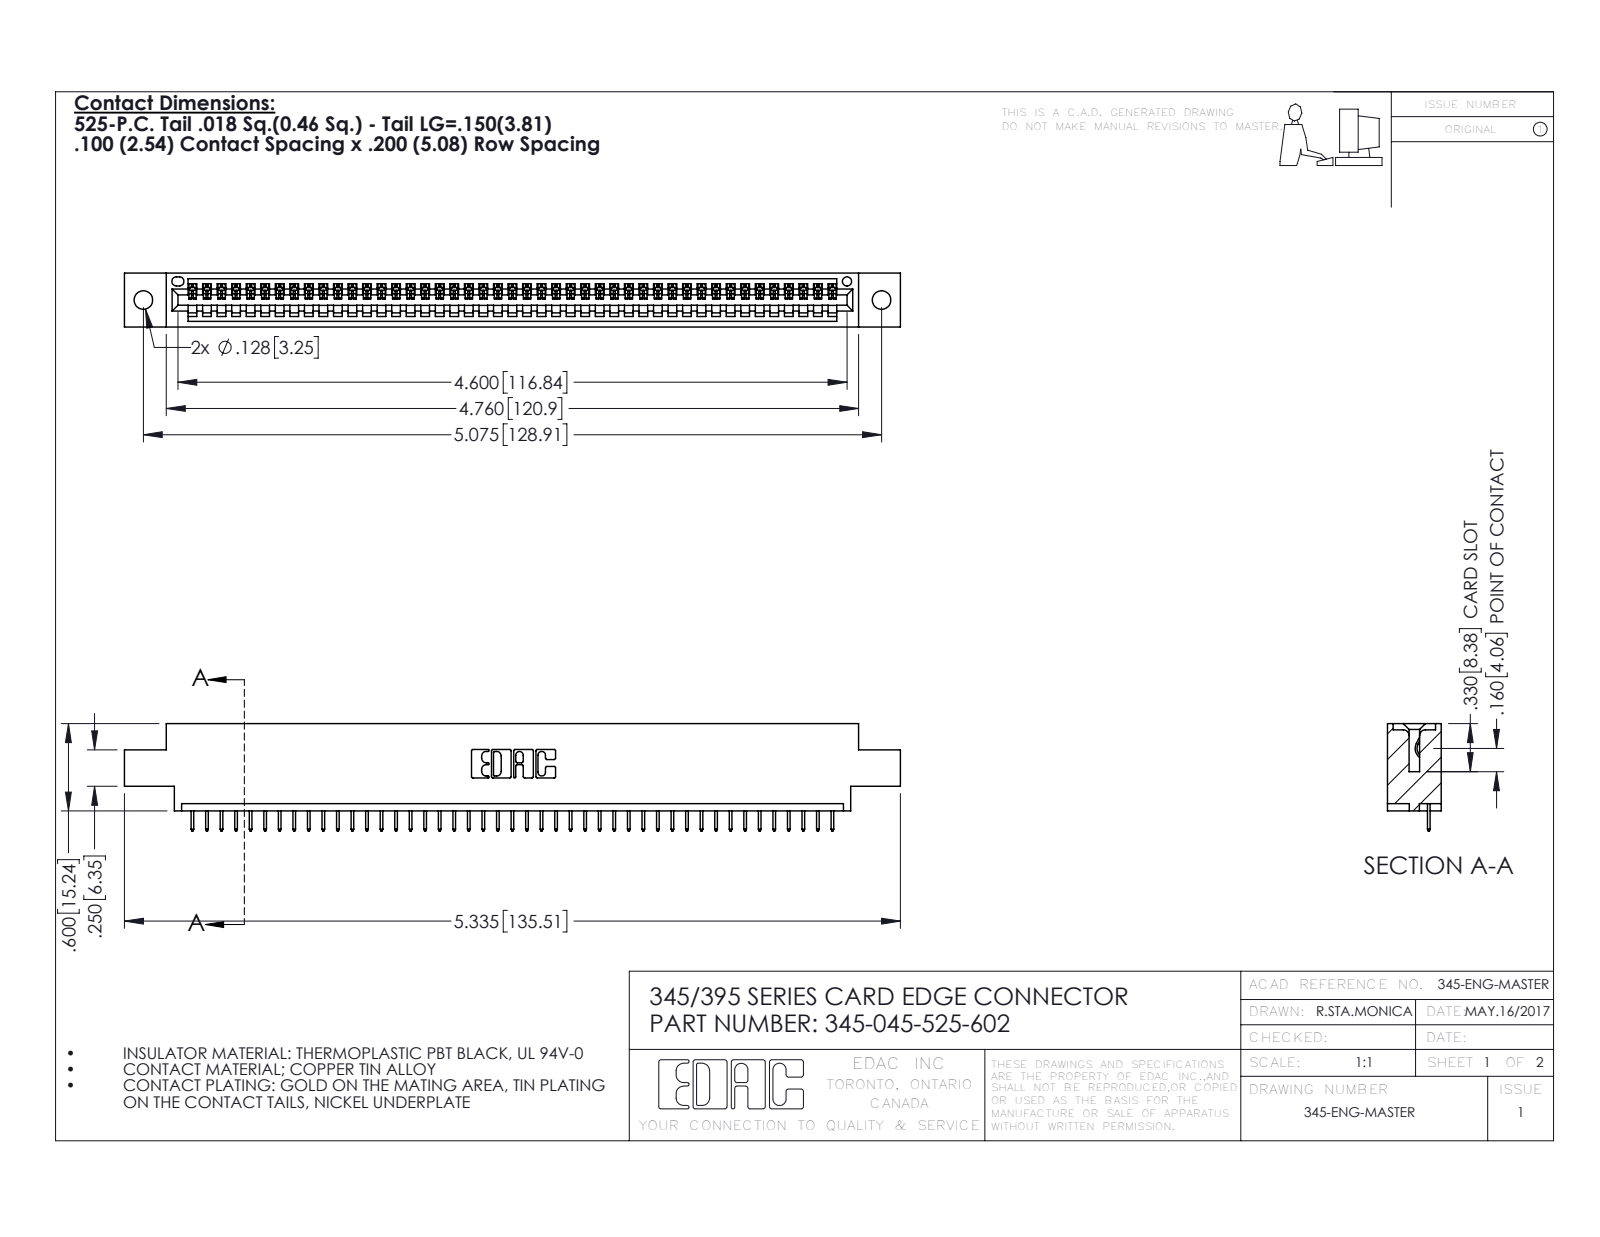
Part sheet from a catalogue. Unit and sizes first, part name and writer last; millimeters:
Units: millimetres
Overall size (bounding box): 135.5 × 18.7 × 9.4
Round holes (diameter × count): ⌀3.3 ×2, ⌀1.6 ×1
Partial cylindrical surfaces — rounded edges, fillets, slot ends (radius × count): R0.2 ×90, R0.3 ×22, R0.2 ×6, R0.8 ×6, R0.7 ×3, R0.8 ×2, R1 ×2, R0.4 ×1
Main face-to-face distances: 1.8, 7.6, 9.4, 5.1, 2.5, 6.9, 0.6, 5.7, 1.8, 4.4
Hole centre spacings: 6.9, 122.9, 128.9
Volume: 12 600 mm³ · Surface area: 15 970 mm²
Bodies: 46 solids, 2920 faces (2154 planar, 766 cylindrical, 0 other)
Part name (STEP PRODUCT): 345-292-001_345-293-125; 345-045-525-602; 345 Part_0.170 Offset - 0.128 Dia
STEP written by: SolidWorks 2020 (CONFIG_CONTROL_DESIGN)
